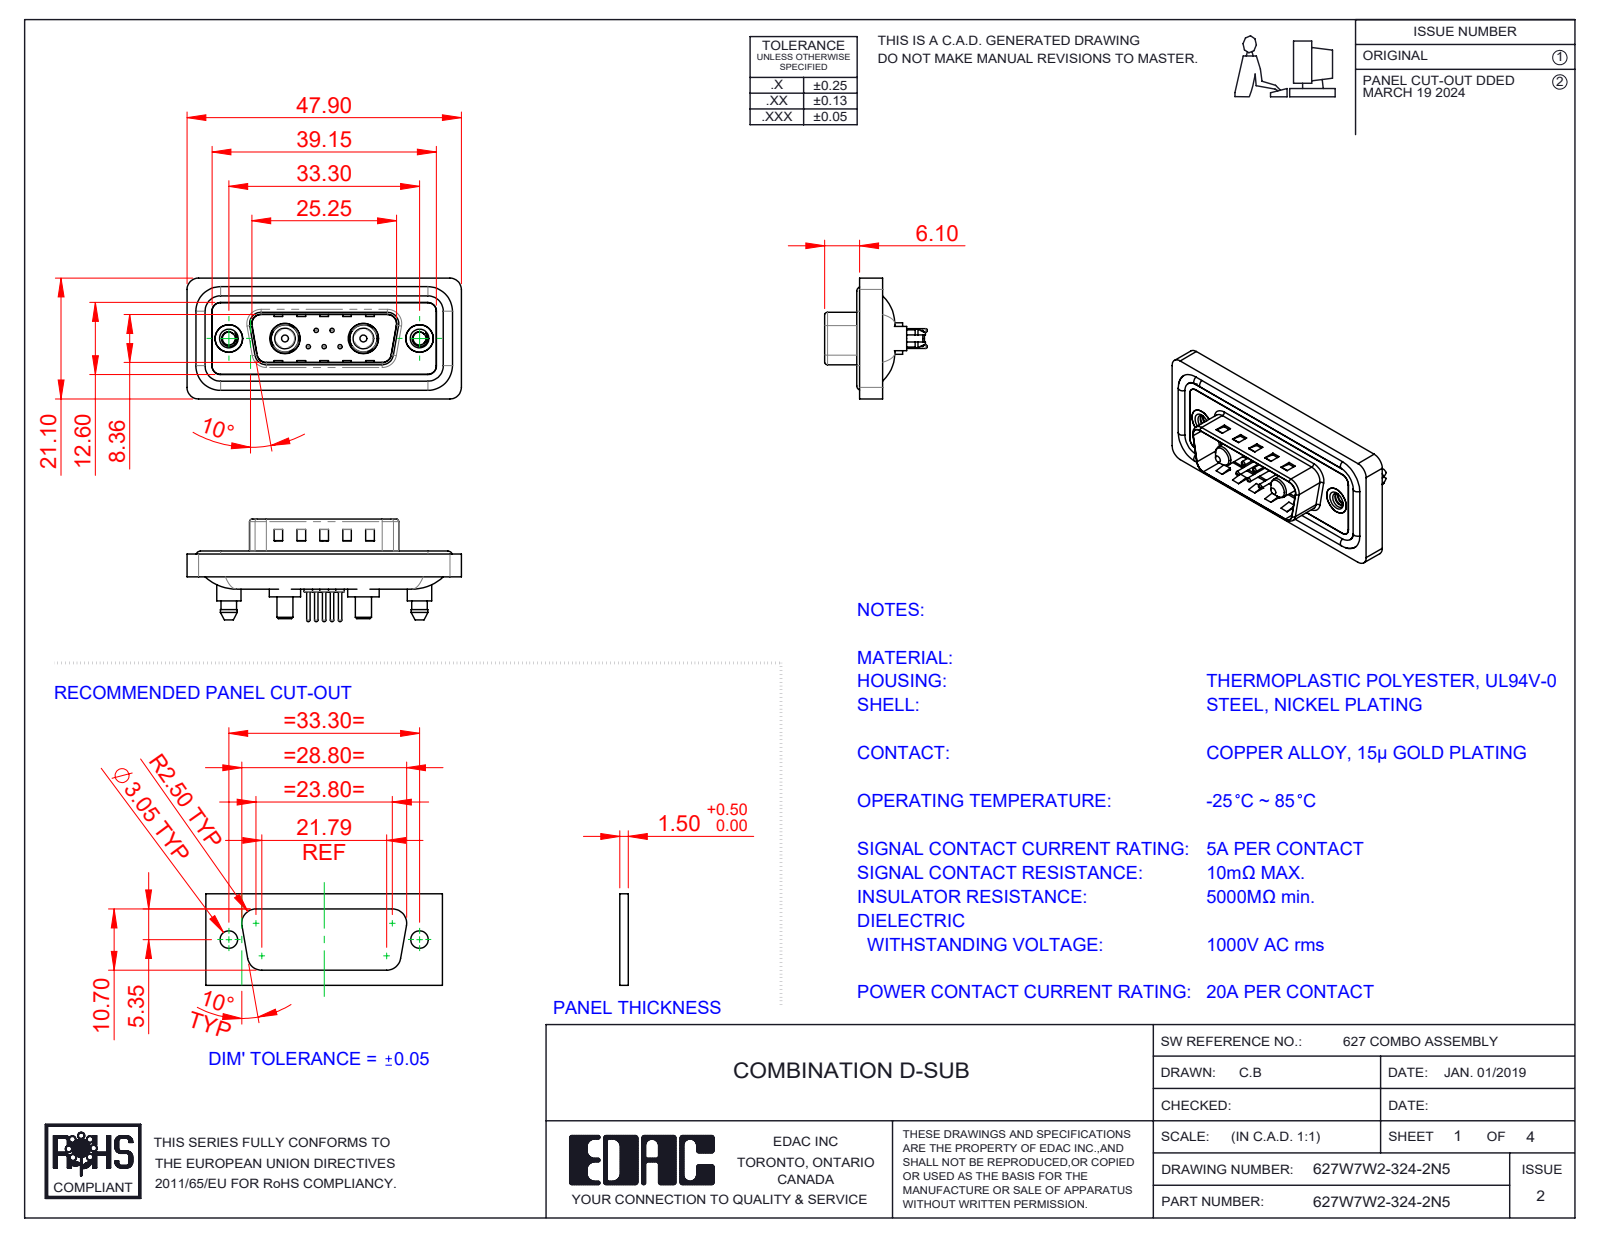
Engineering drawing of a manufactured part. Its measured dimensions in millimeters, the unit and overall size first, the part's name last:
Units: millimetres
Overall size (bounding box): 47.9 × 21.1 × 17.9
Round holes (diameter × count): ⌀0.75 ×5, ⌀1.6 ×5, ⌀2 ×5, ⌀2.26 ×2, ⌀4 ×2, ⌀4.8 ×2, ⌀4.85 ×2, ⌀5 ×2, ⌀5.3 ×2
Round bosses / shafts (diameter × count): ⌀1.5 ×5, ⌀0.6 ×5, ⌀1.6 ×4, ⌀5.5 ×2, ⌀5.4 ×2, ⌀5.2 ×2, ⌀4.9 ×2, ⌀4.75 ×2
Partial cylindrical surfaces — rounded edges, fillets, slot ends (radius × count): R1.5 ×28, R2 ×20, R1.6 ×10, R0.5 ×8, R0.25 ×4, R0.6 ×4, R0.65 ×4, R0.9 ×4
Main face-to-face distances: 0.4, 1.1, 1.5, 1.6, 0.5, 3.1, 2.9, 4, 0.7, 0.82
Hole centre spacings: 3.16, 2.77, 9.8, 23.5, 4.31, 4.33, 5.03, 5.04
Volume: 5 650 mm³ · Surface area: 9 126 mm²
Bodies: 16 solids, 760 faces (248 planar, 324 cylindrical, 188 other)
Part name (STEP PRODUCT): 627Combo Contact Row 1_24; 627Combo Housing_7W2; 627W7W2-324-2N5; 627Combo Shell Rear_15 Contacts (+5 more)
STEP written by: SolidWorks 2023 (CONFIG_CONTROL_DESIGN)
